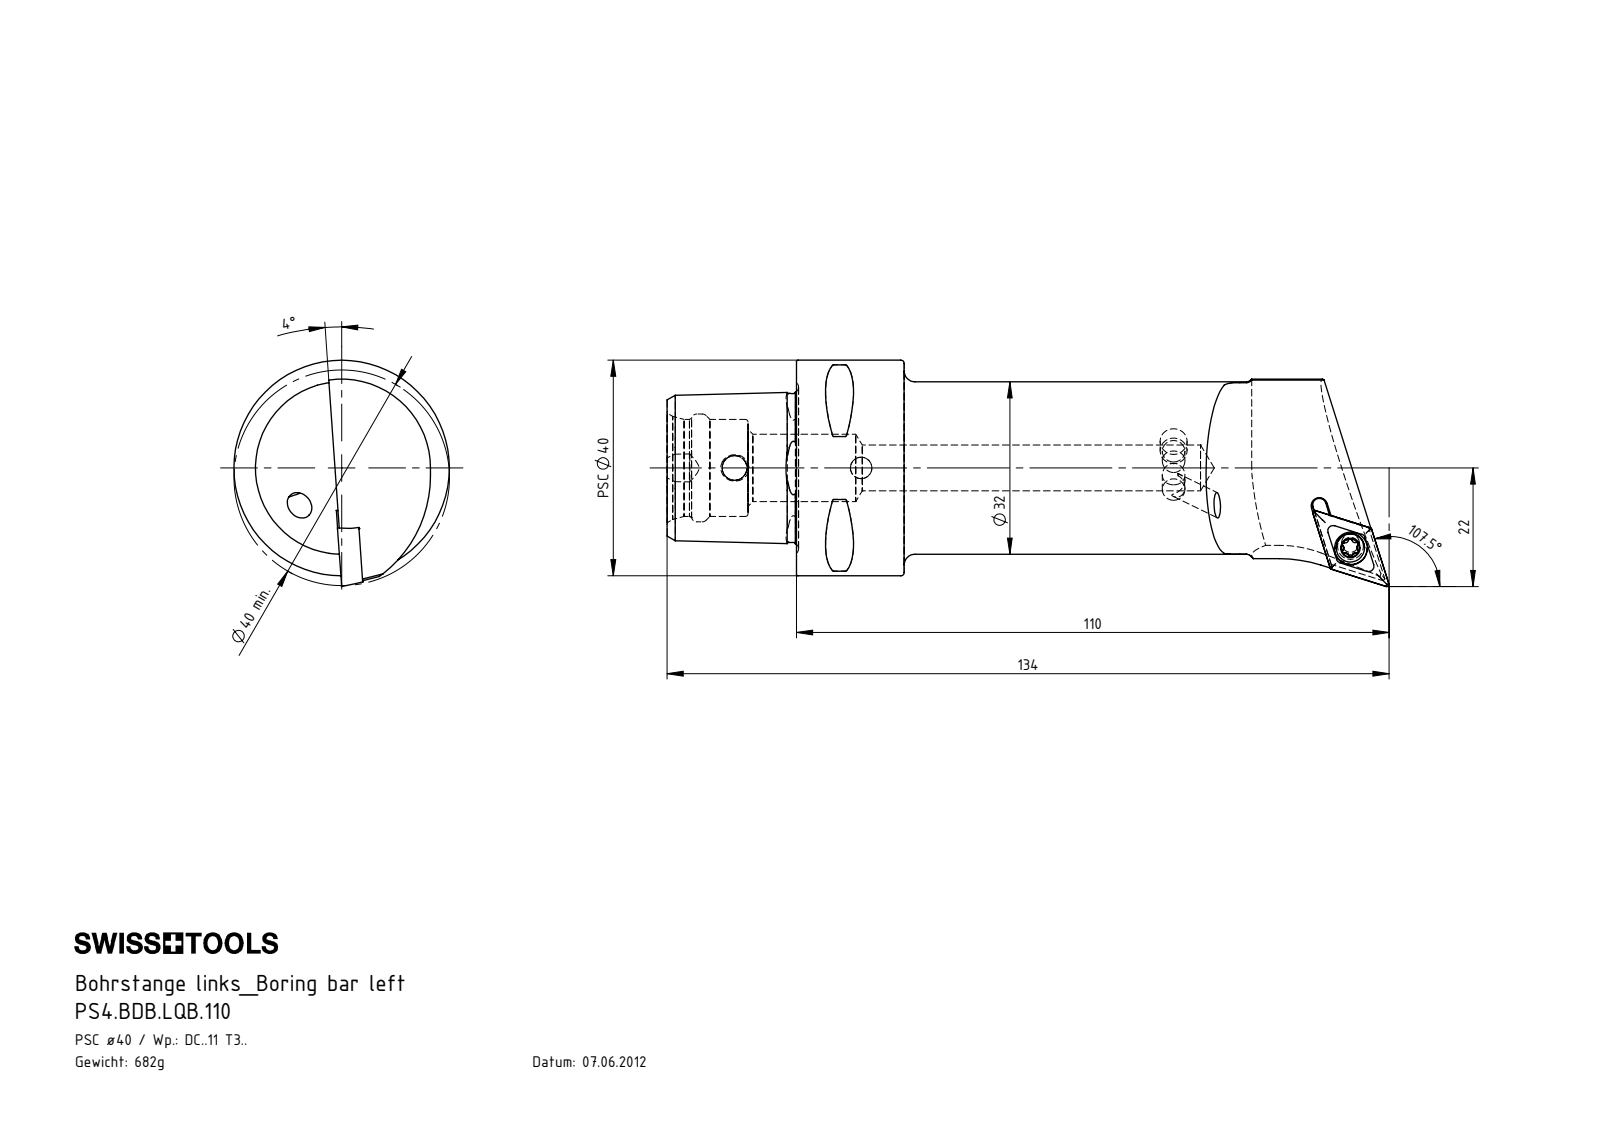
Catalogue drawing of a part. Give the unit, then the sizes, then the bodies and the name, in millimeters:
Units: millimetres
Overall size (bounding box): 134 × 42 × 40
Round holes (diameter × count): ⌀4 ×2, ⌀4.2 ×2, ⌀3.3 ×1, ⌀4.4 ×1, ⌀4.6 ×1, ⌀6.1 ×1, ⌀8.5 ×1, ⌀12.5 ×1, ⌀18 ×1, ⌀20 ×1
Round bosses / shafts (diameter × count): ⌀40 ×1, ⌀32 ×1, ⌀5.25 ×1, ⌀5 ×1, ⌀4 ×1
Partial cylindrical surfaces — rounded edges, fillets, slot ends (radius × count): R0.3 ×8, R0.34 ×6, R0.59 ×6, R3 ×2, R1.25 ×1, R16.5 ×1, R23 ×1, R26 ×1
Main face-to-face distances: 20, 24, 44, 3.67, 15.52, 35.3, 15, 9, 29, 23.8
Hole centre spacings: 23.5
Volume: 86 653 mm³ · Surface area: 19 730 mm²
Bodies: 5 solids, 298 faces (53 planar, 75 cylindrical, 170 other)
Part name (STEP PRODUCT): KVT_MB_600_050; WCB-ER2.001.009_A; PS4.BDB.LQB.110; DCMT11T304 (+1 more)
STEP written by: SolidWorks 2017 (AUTOMOTIVE_DESIGN)
